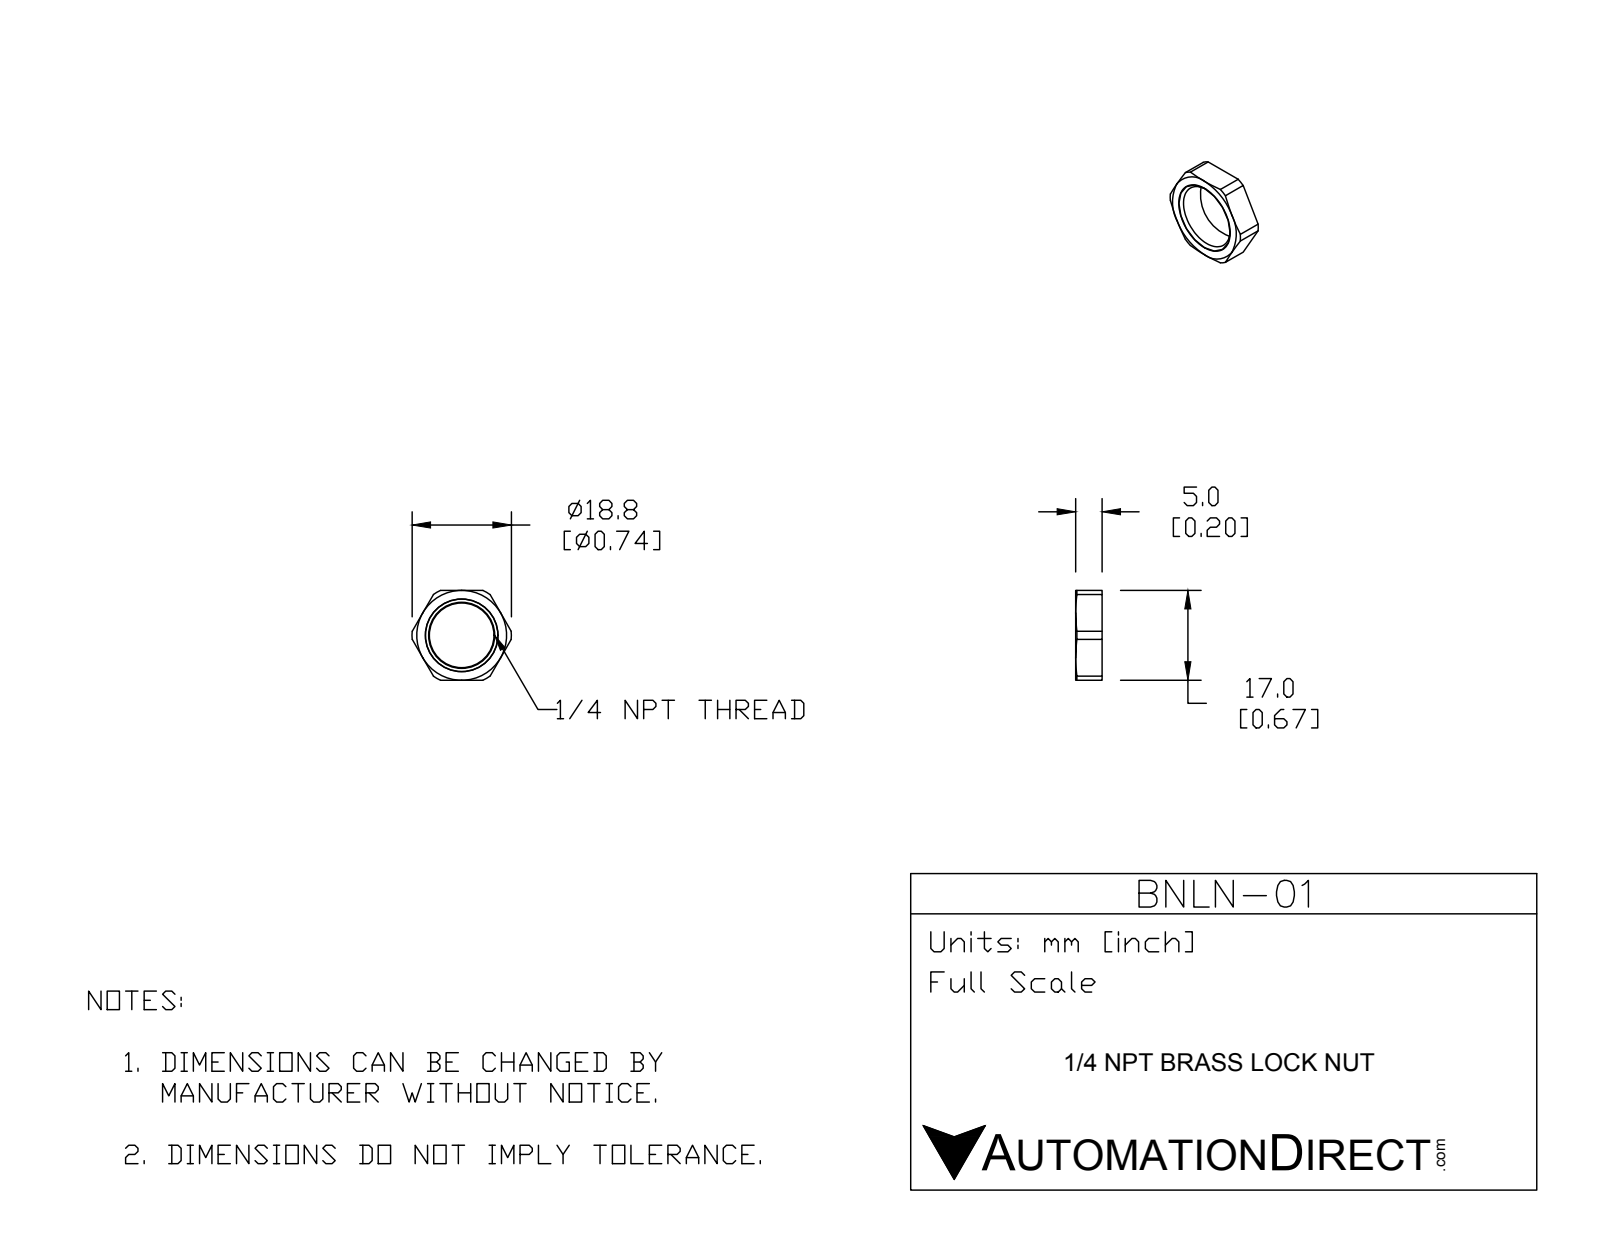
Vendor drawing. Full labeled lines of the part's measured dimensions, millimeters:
Part name (STEP PRODUCT): BNLN-01
STEP written by: SolidWorks 2015 (CONFIG_CONTROL_DESIGN)
Units: millimetres
Bodies: 1 solid, 25 faces (8 planar, 7 cylindrical, 10 other)
Overall size (bounding box): 18.8 × 17 × 5
Volume: 631 mm³ · Surface area: 719 mm²
Partial cylindrical surfaces — rounded edges, fillets, slot ends (radius × count): R9.4 ×1
Main face-to-face distances: 17, 5
